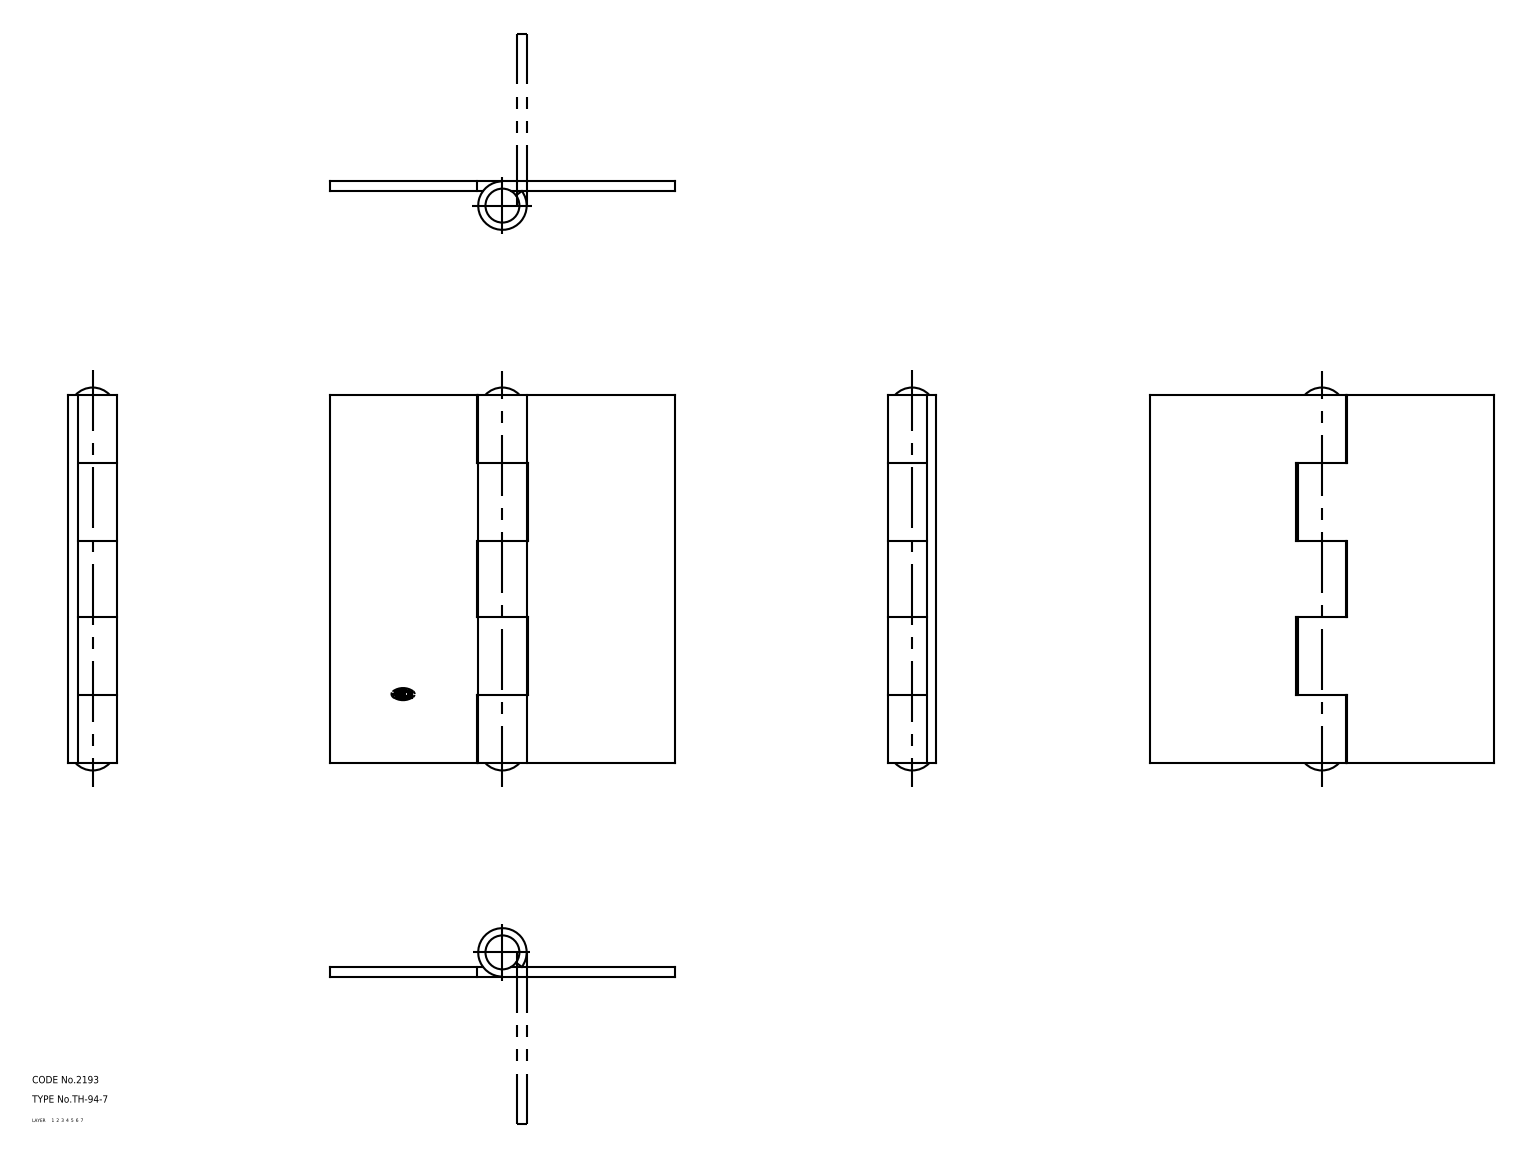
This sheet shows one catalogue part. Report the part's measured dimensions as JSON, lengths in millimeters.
{"part_name": "hinge piece_B; hinge piece_A; shaft; TH_94_7_19175_36", "step_written_by": "CADfix (AUTOMOTIVE_DESIGN)", "units": "millimeters", "bodies": {"solids": 3, "faces": 44, "planar": 0, "cylindrical": 0, "other": 44}, "overall_size": [157.97, 142, 20], "volume_mm3": 123678, "surface_area_mm2": 64695}
